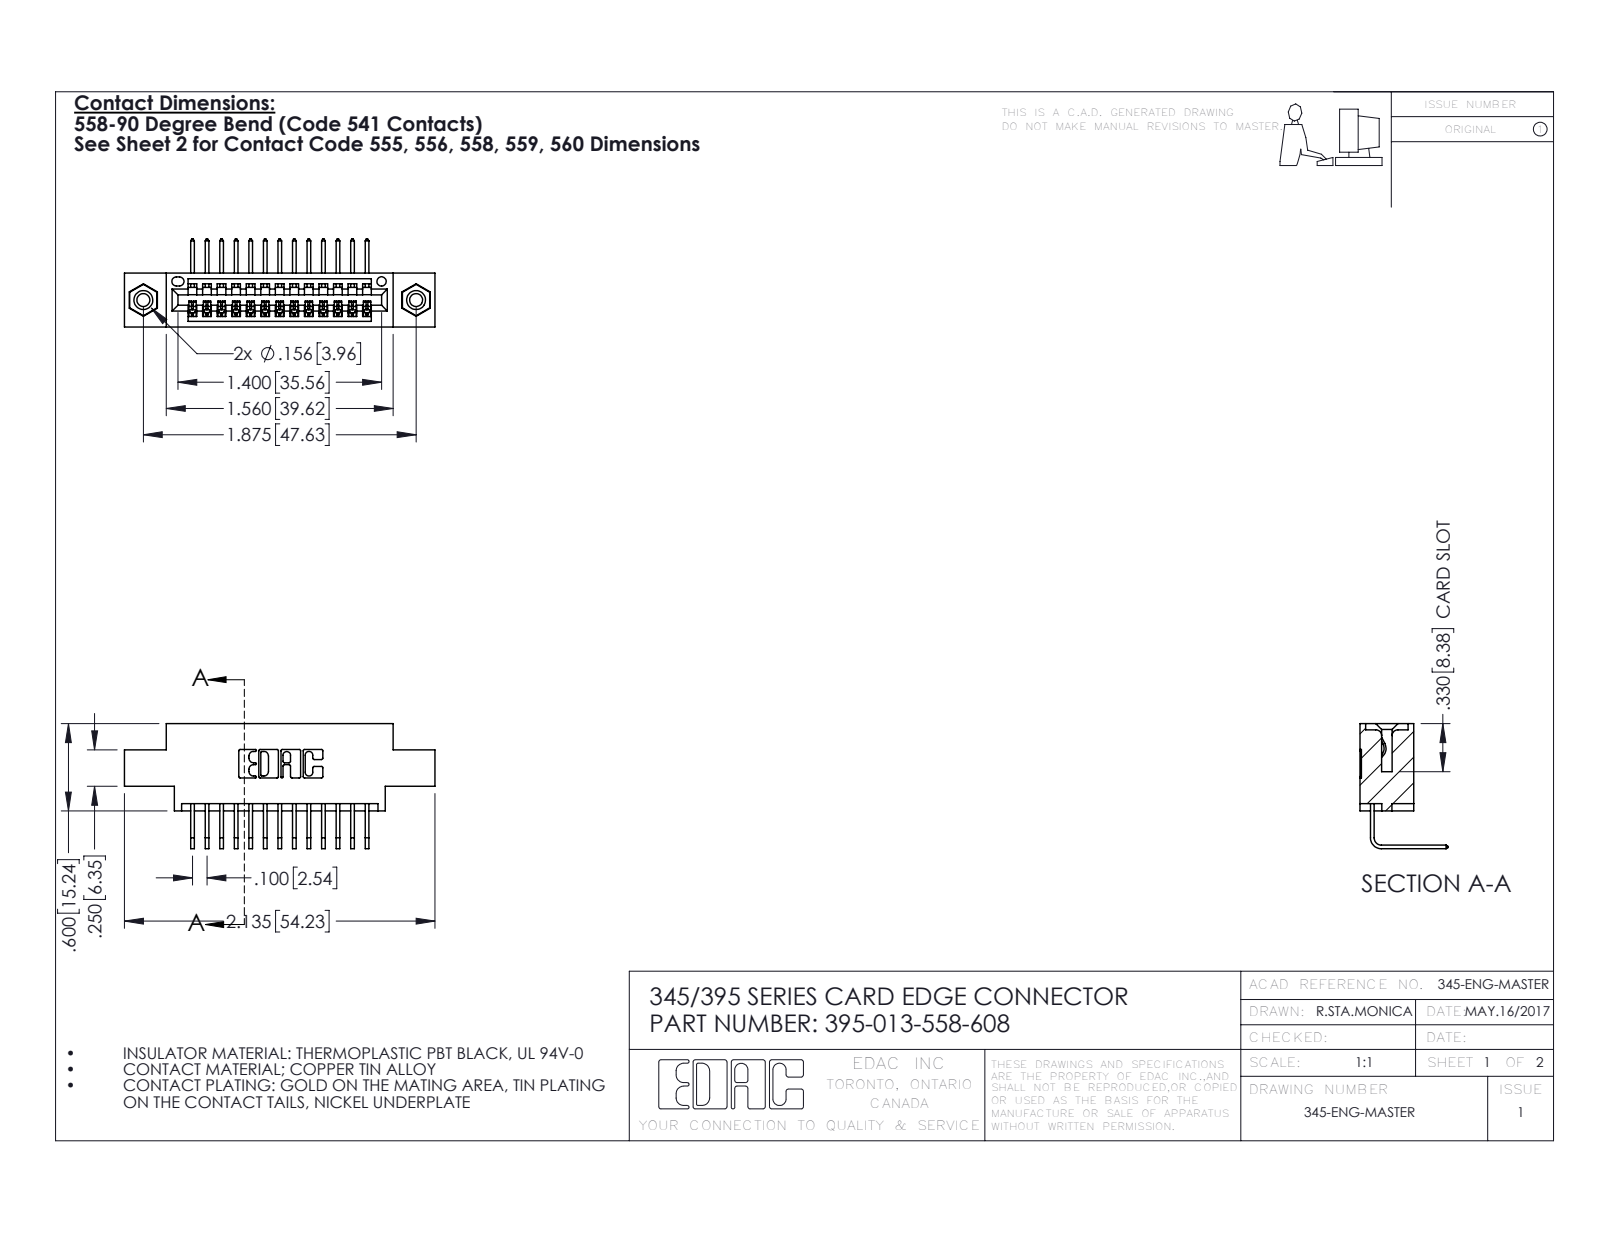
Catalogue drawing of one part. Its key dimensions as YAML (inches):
part_name: "345 Part_0.170 Offset - 0.156 Dia-TI; 345-292-001_558 Tail - 2; 395-013-558-608; 345-250-001_345-250-003-102"
step_written_by: "SolidWorks 2016 (CONFIG_CONTROL_DESIGN)"
units: inches
bodies: {solids: 16, faces: 970, planar: 662, cylindrical: 292, other: 16}
overall_size: [2.135, 0.859, 0.605]
volume: 0.295
surface_area: 9.972
round_holes:
  - {diameter: 0.089, count: 2}
  - {diameter: 0.125, count: 2}
  - {diameter: 0.156, count: 2}
  - {diameter: 0.064, count: 1}
round_bosses_or_shafts:
  - {diameter: 0.155, count: 2}
partial_cylinders:
  - {radius: 0.006, count: 26}
  - {radius: 0.01, count: 22}
  - {radius: 0.007, count: 6}
  - {radius: 0.031, count: 6}
  - {radius: 0.026, count: 3}
  - {radius: 0.031, count: 2}
  - {radius: 0.04, count: 2}
  - {radius: 0.014, count: 1}
face_to_face_distances: [0.37, 0.072, 0.298, 0.2, 0.098, 0.272, 0.025, 0.1, 0.225, 0.15]
hole_center_spacings: [0.27, 1.643, 1.875]
